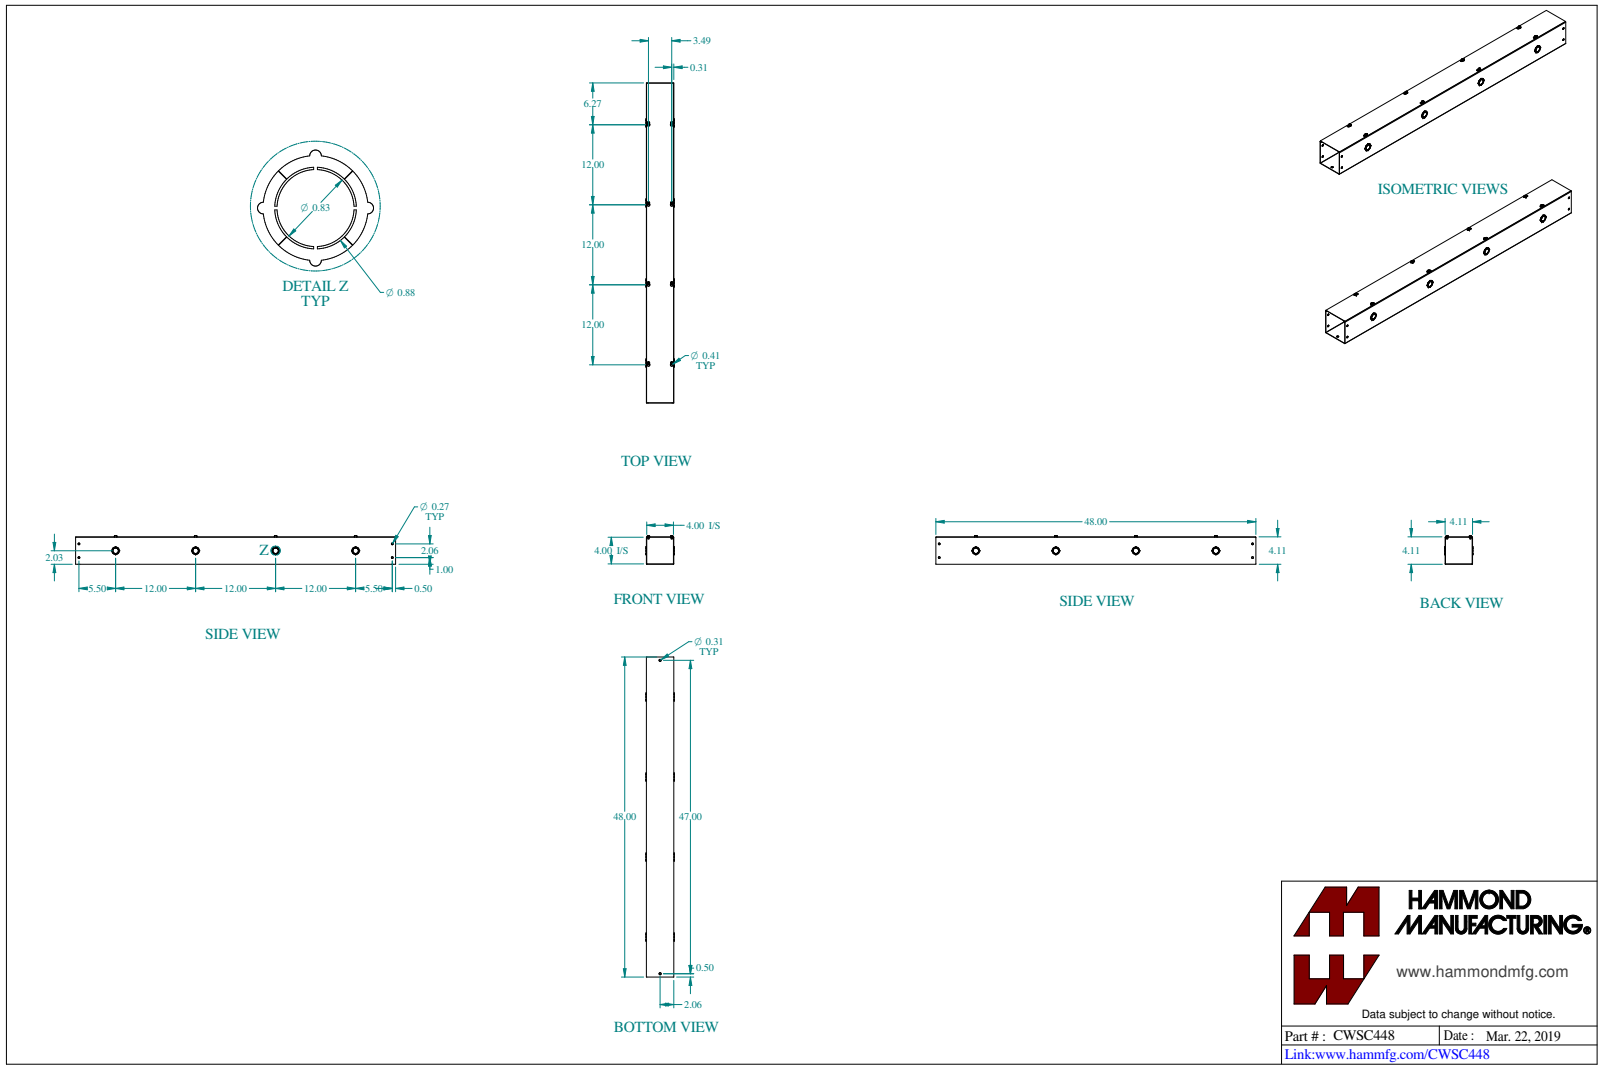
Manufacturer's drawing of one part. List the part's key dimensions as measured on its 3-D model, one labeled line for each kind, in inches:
Part name (STEP PRODUCT): CWSC448
STEP written by: SolidWorks 2023 (CONFIG_CONTROL_DESIGN)
Units: inches
Bodies: 10 solids, 640 faces (284 planar, 308 cylindrical, 48 other)
Overall size (bounding box): 48 × 4.289 × 4.258
Volume: 46.93 in³ · Surface area: 1 645 in²
Round holes (diameter × count): ⌀0.177 ×8, ⌀0.266 ×4, ⌀0.875 ×4, ⌀0.313 ×2
Round bosses / shafts (diameter × count): ⌀0.375 ×8, ⌀0.19 ×8, ⌀1.125 ×4, ⌀1.125 ×4, ⌀0.825 ×4
Partial cylindrical surfaces — rounded edges, fillets, slot ends (radius × count): R0.062 ×12, R0.125 ×8, R0.203 ×8, R0.029 ×4, R0.063 ×4, R0.086 ×4
Main face-to-face distances: 0.057, 4.057, 4, 4.114, 3.943, 0.114, 0.072, 0.129, 4.129, 4.186
Hole centre spacings: 12, 12.497, 24, 3.489, 5.595, 5.77, 17.53, 17.587
